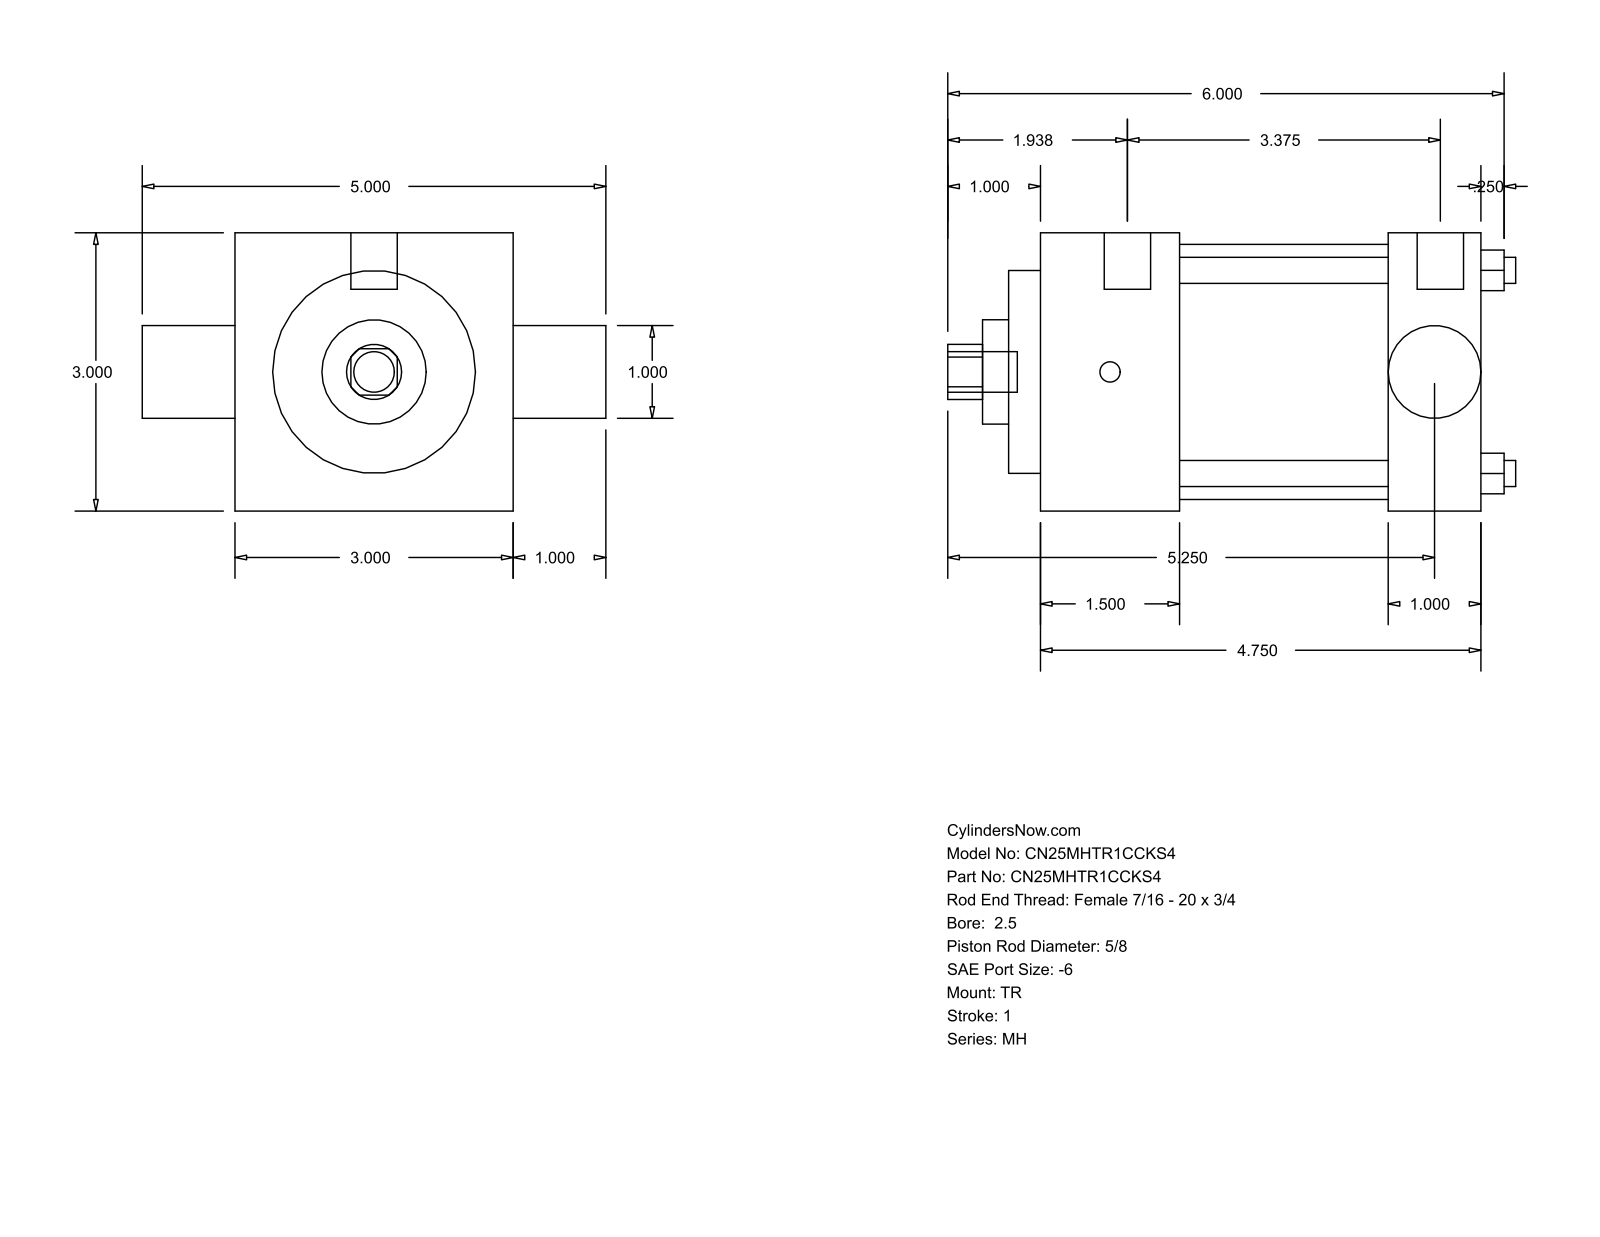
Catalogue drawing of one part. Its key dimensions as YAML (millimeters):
part_name: "MH_TR__0250_0.625"
step_written_by: "GSSL Pune (CONFIG_CONTROL_DESIGN)"
units: millimeters
bodies: {solids: 0, faces: 86, planar: 61, cylindrical: 25, other: 0}
overall_size: [155.57, 127, 76.2]
round_holes:
  - {diameter: 7.14, count: 4}
  - {diameter: 15.88, count: 1}
  - {diameter: 25.35, count: 1}
  - {diameter: 28.57, count: 1}
  - {diameter: 55.55, count: 1}
  - {diameter: 69.85, count: 1}
round_bosses_or_shafts:
  - {diameter: 5.56, count: 3}
  - {diameter: 12.7, count: 2}
  - {diameter: 11.11, count: 1}
partial_cylinders:
  - {radius: 7.54, count: 1}
face_to_face_distances: [76.2, 120.65, 25.4, 57.15, 38.1, 82.55, 95.25, 8.73, 46.83, 103.98]
hole_center_spacings: [39.33, 55.62, 78.66]
